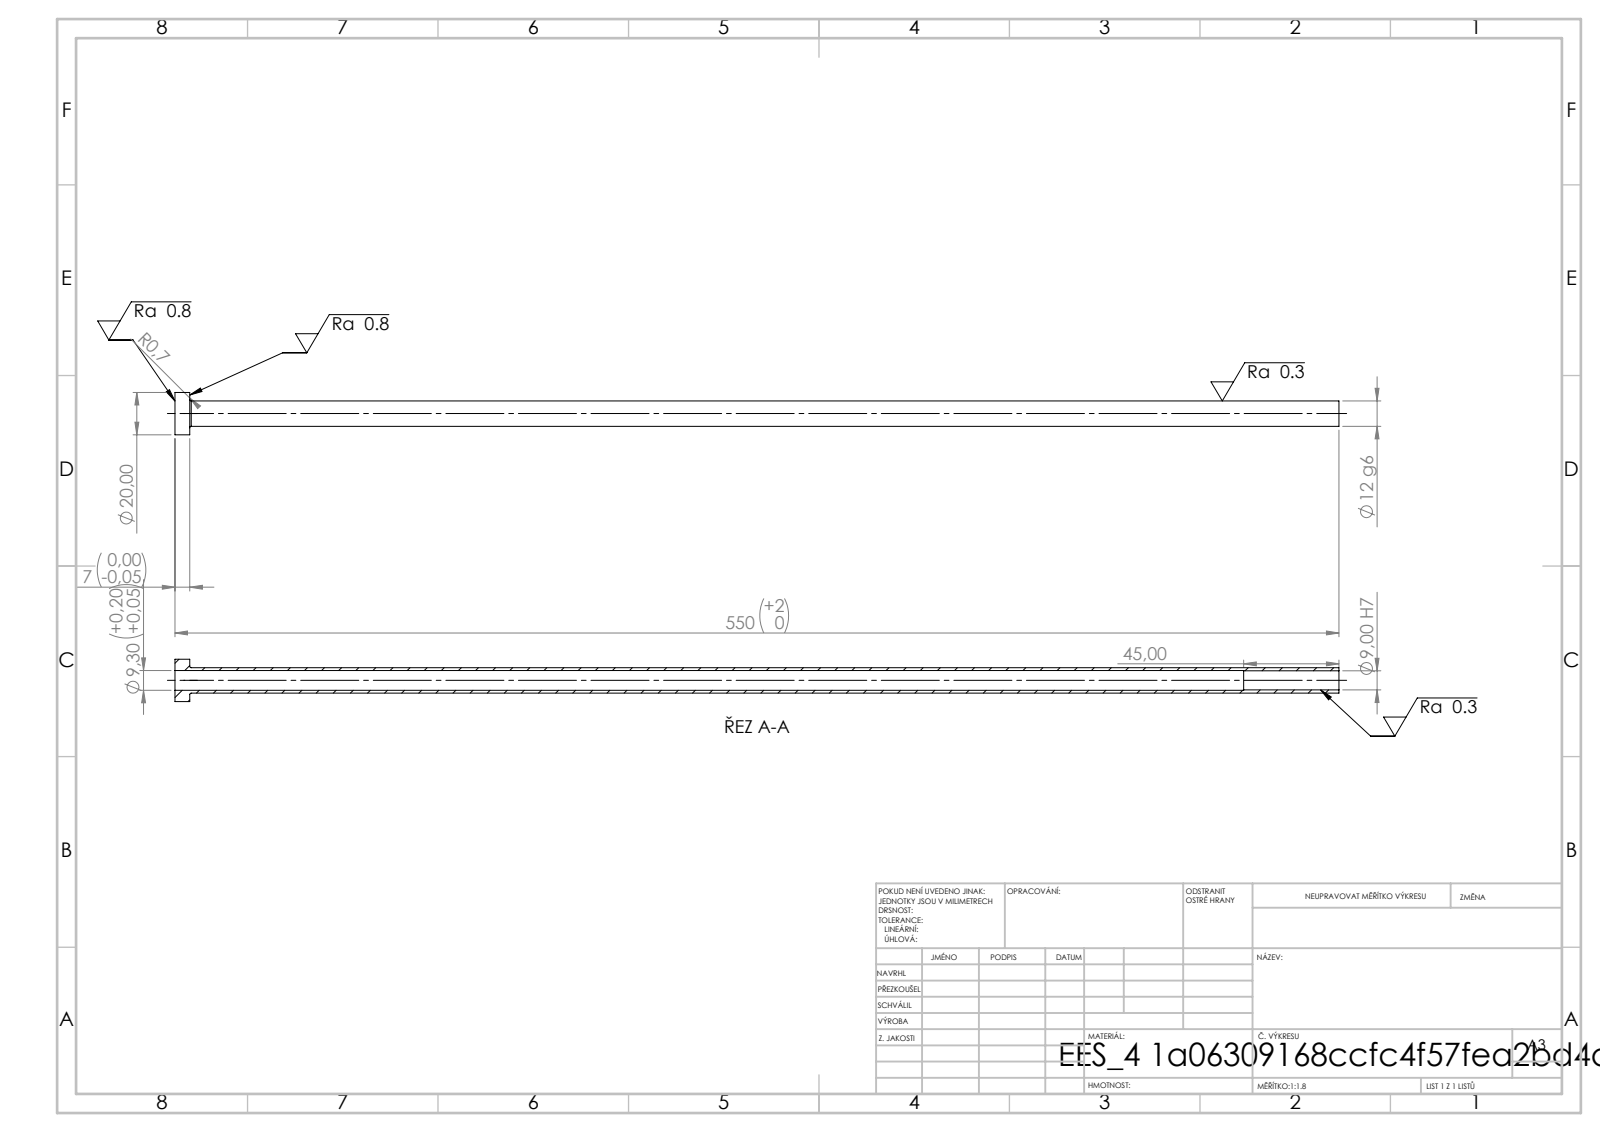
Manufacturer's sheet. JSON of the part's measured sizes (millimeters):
{"step_written_by": "SolidWorks 2019 (CONFIG_CONTROL_DESIGN)", "units": "millimeters", "bodies": {"solids": 1, "faces": 14, "planar": 4, "cylindrical": 8, "other": 2}, "overall_size": [550, 20, 20], "volume_mm3": 26448, "surface_area_mm2": 37427, "round_holes": [[9, 1], [9.3, 1]], "round_bosses_or_shafts": [[20, 1], [12, 1]], "face_to_face_distances": [7, 550, 543, 505, 498, 45]}
